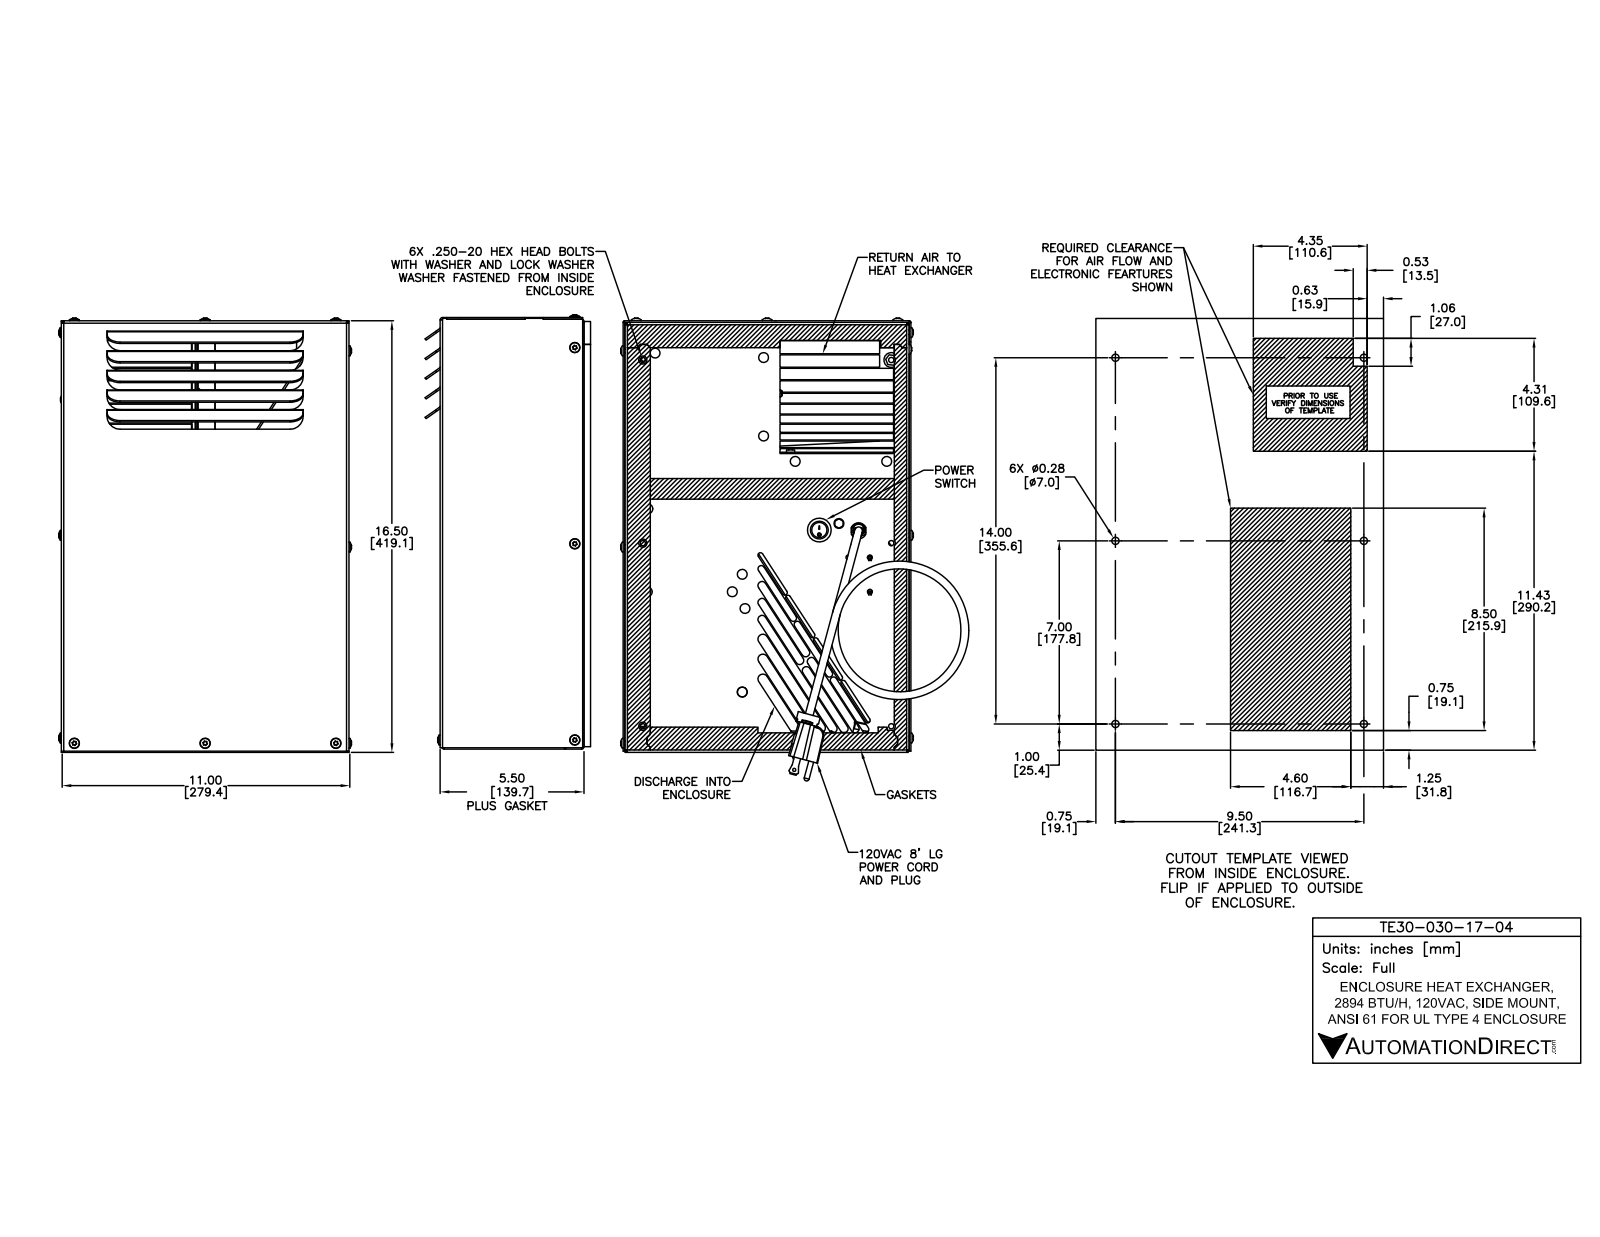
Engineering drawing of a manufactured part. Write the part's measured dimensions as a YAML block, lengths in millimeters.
part_name: "TE30-030-17-04"
step_written_by: "SolidWorks 2017 (AUTOMOTIVE_DESIGN)"
units: millimeters
bodies: {solids: 122, faces: 3166, planar: 1807, cylindrical: 975, other: 384}
overall_size: [421.5, 284.2, 164.2]
volume: 2796000
surface_area: 2001000
round_holes:
  - {diameter: 4.8, count: 23}
  - {diameter: 4.9, count: 23}
  - {diameter: 5.6, count: 19}
  - {diameter: 12.7, count: 16}
  - {diameter: 5.2, count: 9}
  - {diameter: 4, count: 8}
  - {diameter: 2.8, count: 7}
  - {diameter: 5, count: 6}
  - {diameter: 5.1, count: 6}
  - {diameter: 5.1, count: 6}
  - {diameter: 6.4, count: 6}
  - {diameter: 6.9, count: 6}
round_bosses_or_shafts:
  - {diameter: 6.9, count: 23}
  - {diameter: 4.8, count: 15}
  - {diameter: 14.3, count: 6}
  - {diameter: 11.2, count: 6}
  - {diameter: 8.7, count: 6}
  - {diameter: 8.3, count: 6}
  - {diameter: 8.3, count: 6}
  - {diameter: 7.9, count: 6}
partial_cylinders:
  - {radius: 0.3, count: 84}
  - {radius: 0.4, count: 84}
  - {radius: 0.8, count: 59}
  - {radius: 2.4, count: 46}
  - {radius: 2.6, count: 18}
  - {radius: 1.5, count: 17}
  - {radius: 2.4, count: 13}
  - {radius: 3.2, count: 12}
face_to_face_distances: [1.6, 1.6, 276.1, 139.7, 136.6, 138.1, 138.1, 277.7, 274.5, 27.5]
hole_center_spacings: [31.8, 63.5, 95.3, 32.9, 30.6, 64.7, 1.5, 82.6]
